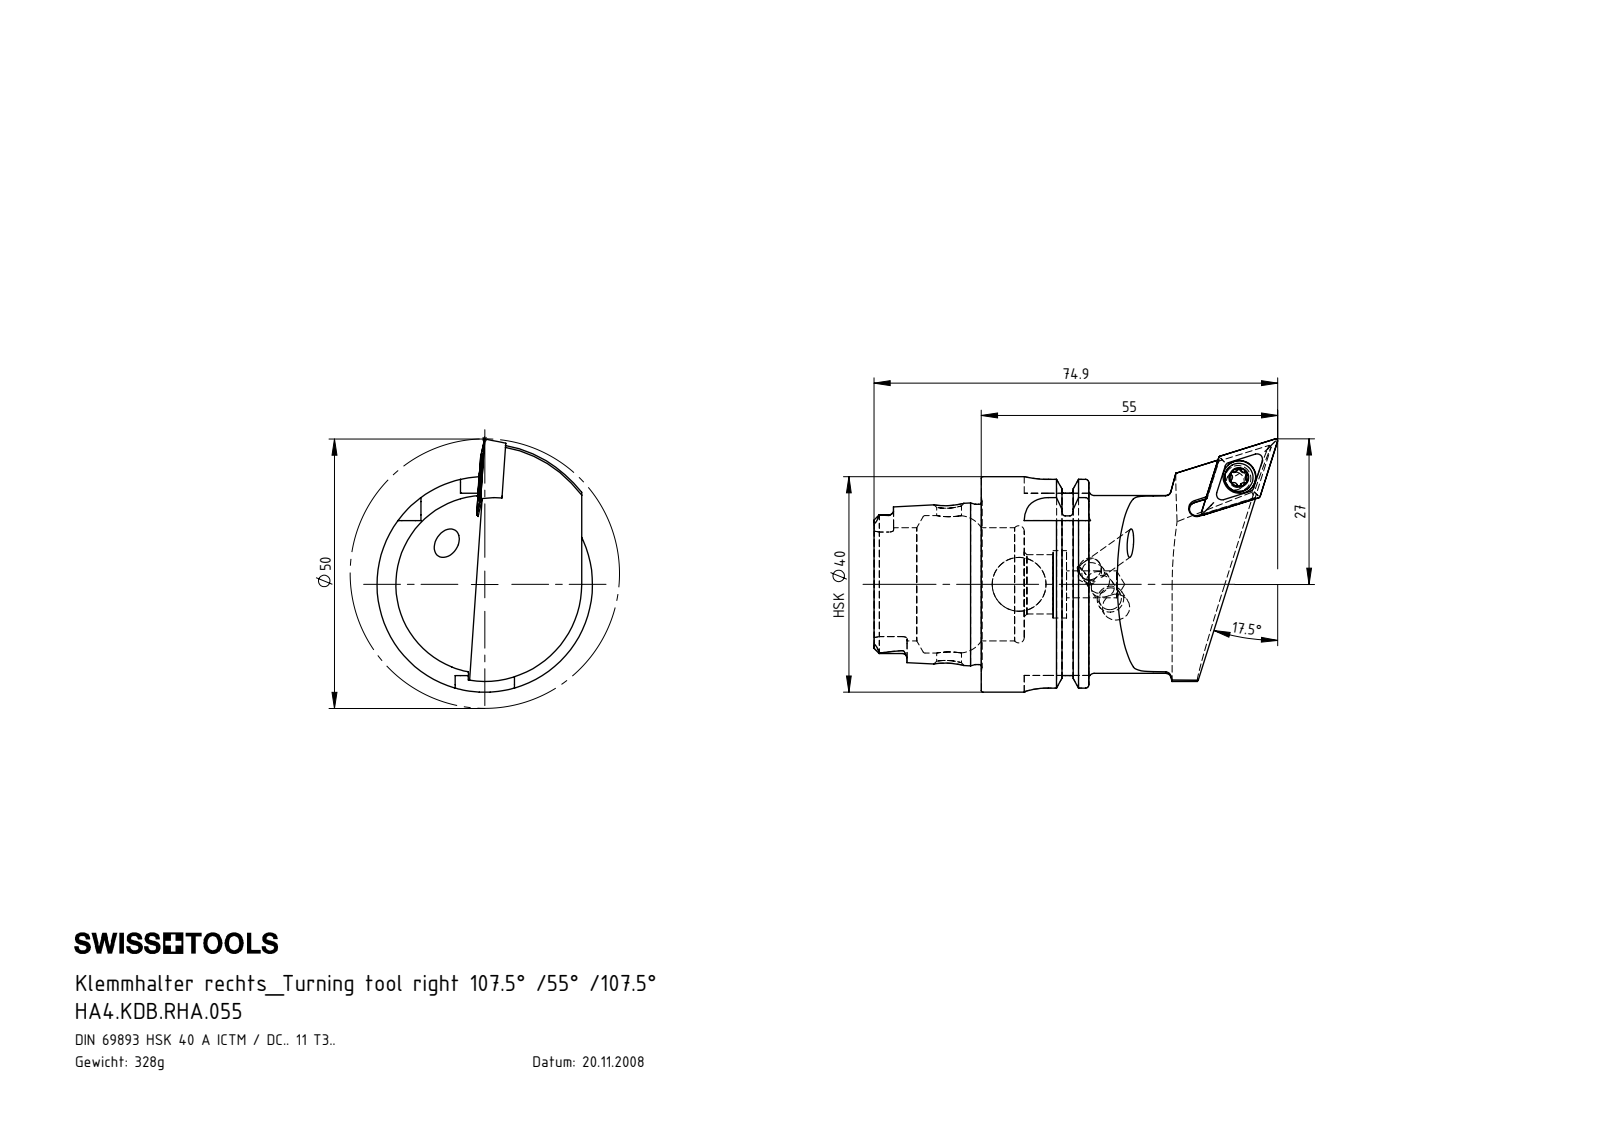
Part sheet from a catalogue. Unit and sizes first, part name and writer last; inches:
Units: inches
Overall size (bounding box): 2.949 × 1.85 × 1.575
Round holes (diameter × count): ⌀0.165 ×2, ⌀0.197 ×2, ⌀0.13 ×1, ⌀0.157 ×1, ⌀0.173 ×1, ⌀0.181 ×1, ⌀0.24 ×1, ⌀0.394 ×1, ⌀0.433 ×1, ⌀0.492 ×1, ⌀0.827 ×1, ⌀1.004 ×1
Round bosses / shafts (diameter × count): ⌀1.575 ×1, ⌀1.368 ×1, ⌀1.299 ×1, ⌀1.17 ×1, ⌀0.207 ×1, ⌀0.197 ×1, ⌀0.157 ×1
Partial cylindrical surfaces — rounded edges, fillets, slot ends (radius × count): R0.013 ×6, R0.023 ×6, R0.035 ×6, R0.177 ×4, R0.072 ×2, R0.074 ×2, R0.049 ×1, R0.118 ×1
Main face-to-face distances: 0.313, 0.785, 0.472, 0.145, 0.783, 1.096, 1.569, 1.406, 0.622, 0.309
Volume: 2.513 in³ · Surface area: 21.34 in²
Bodies: 5 solids, 316 faces (76 planar, 95 cylindrical, 145 other)
Part name (STEP PRODUCT): HA4-KDB.RHA.055_A_Fertigbearbeitung; DCMT11T304; HA4.KDB.RHA.055; KVT_MB_600_050 (+1 more)
STEP written by: SolidWorks 2015 (AUTOMOTIVE_DESIGN)
